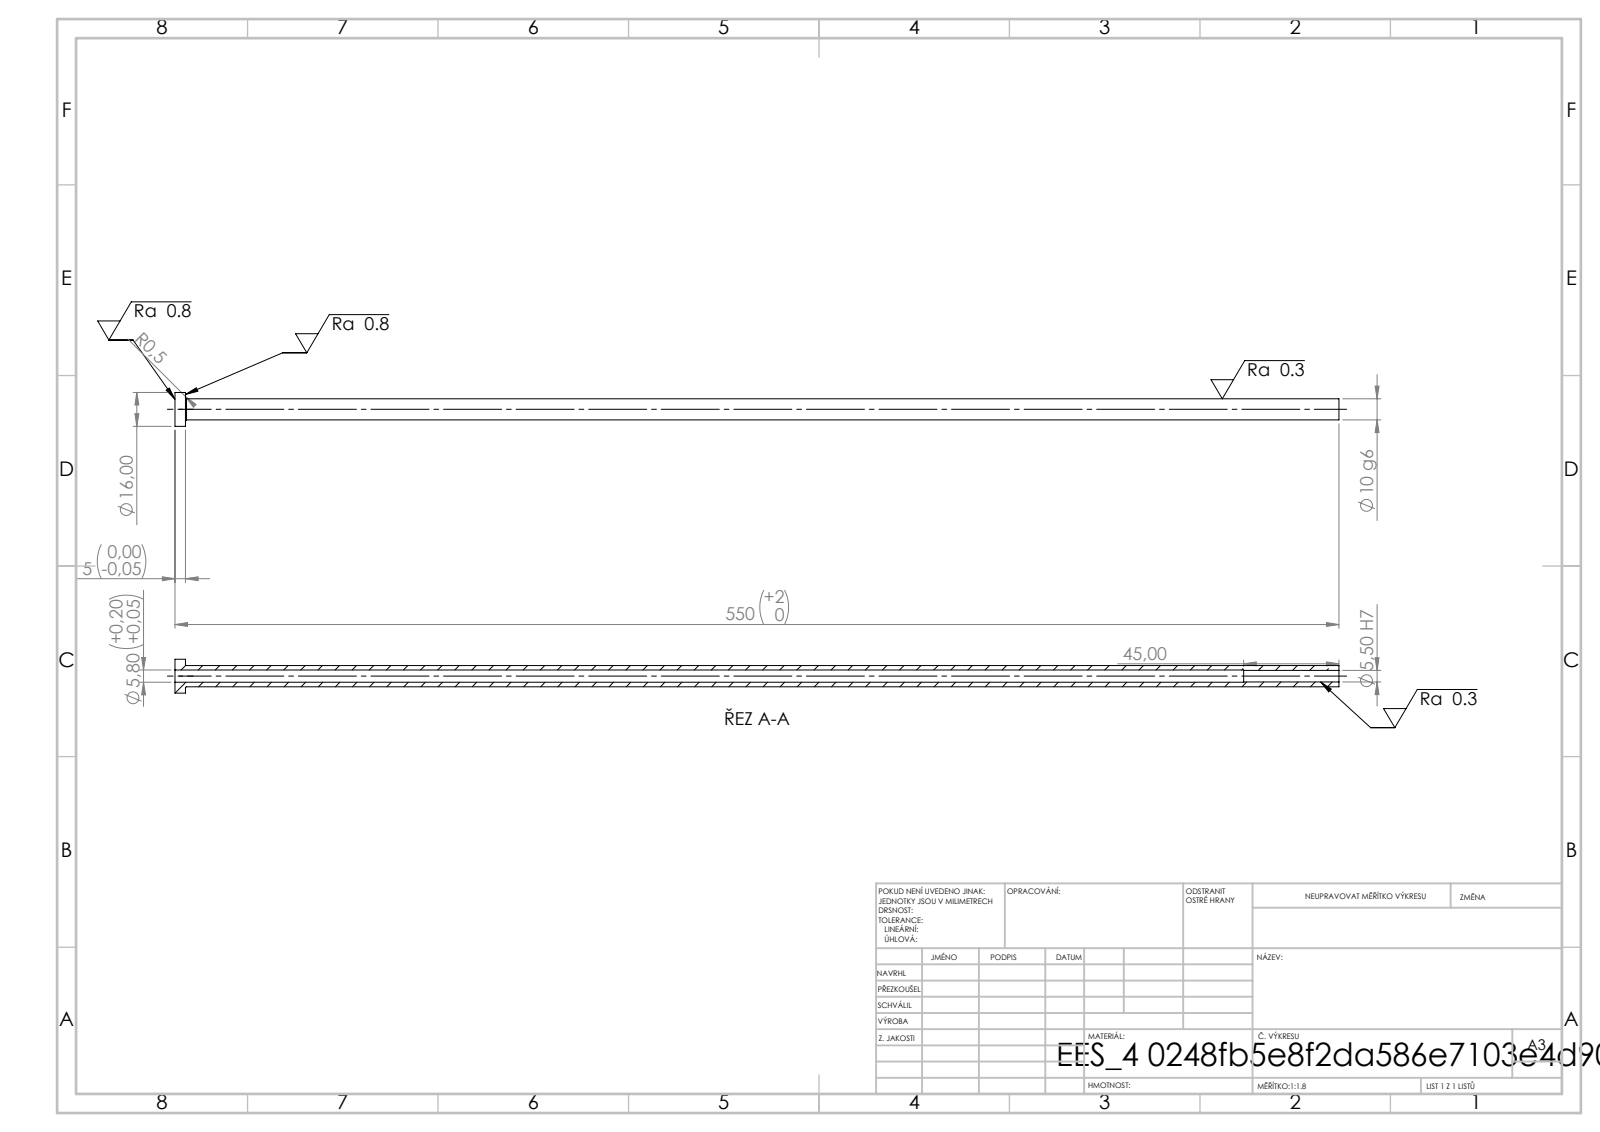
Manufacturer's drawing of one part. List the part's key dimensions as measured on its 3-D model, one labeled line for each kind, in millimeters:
STEP written by: SolidWorks 2019 (CONFIG_CONTROL_DESIGN)
Units: millimetres
Bodies: 1 solid, 14 faces (4 planar, 8 cylindrical, 2 other)
Overall size (bounding box): 550 × 16 × 16
Volume: 29 400 mm³ · Surface area: 27 700 mm²
Round holes (diameter × count): ⌀5.5 ×1, ⌀5.8 ×1
Round bosses / shafts (diameter × count): ⌀16 ×1, ⌀10 ×1
Main face-to-face distances: 5, 550, 545, 505, 500, 45
